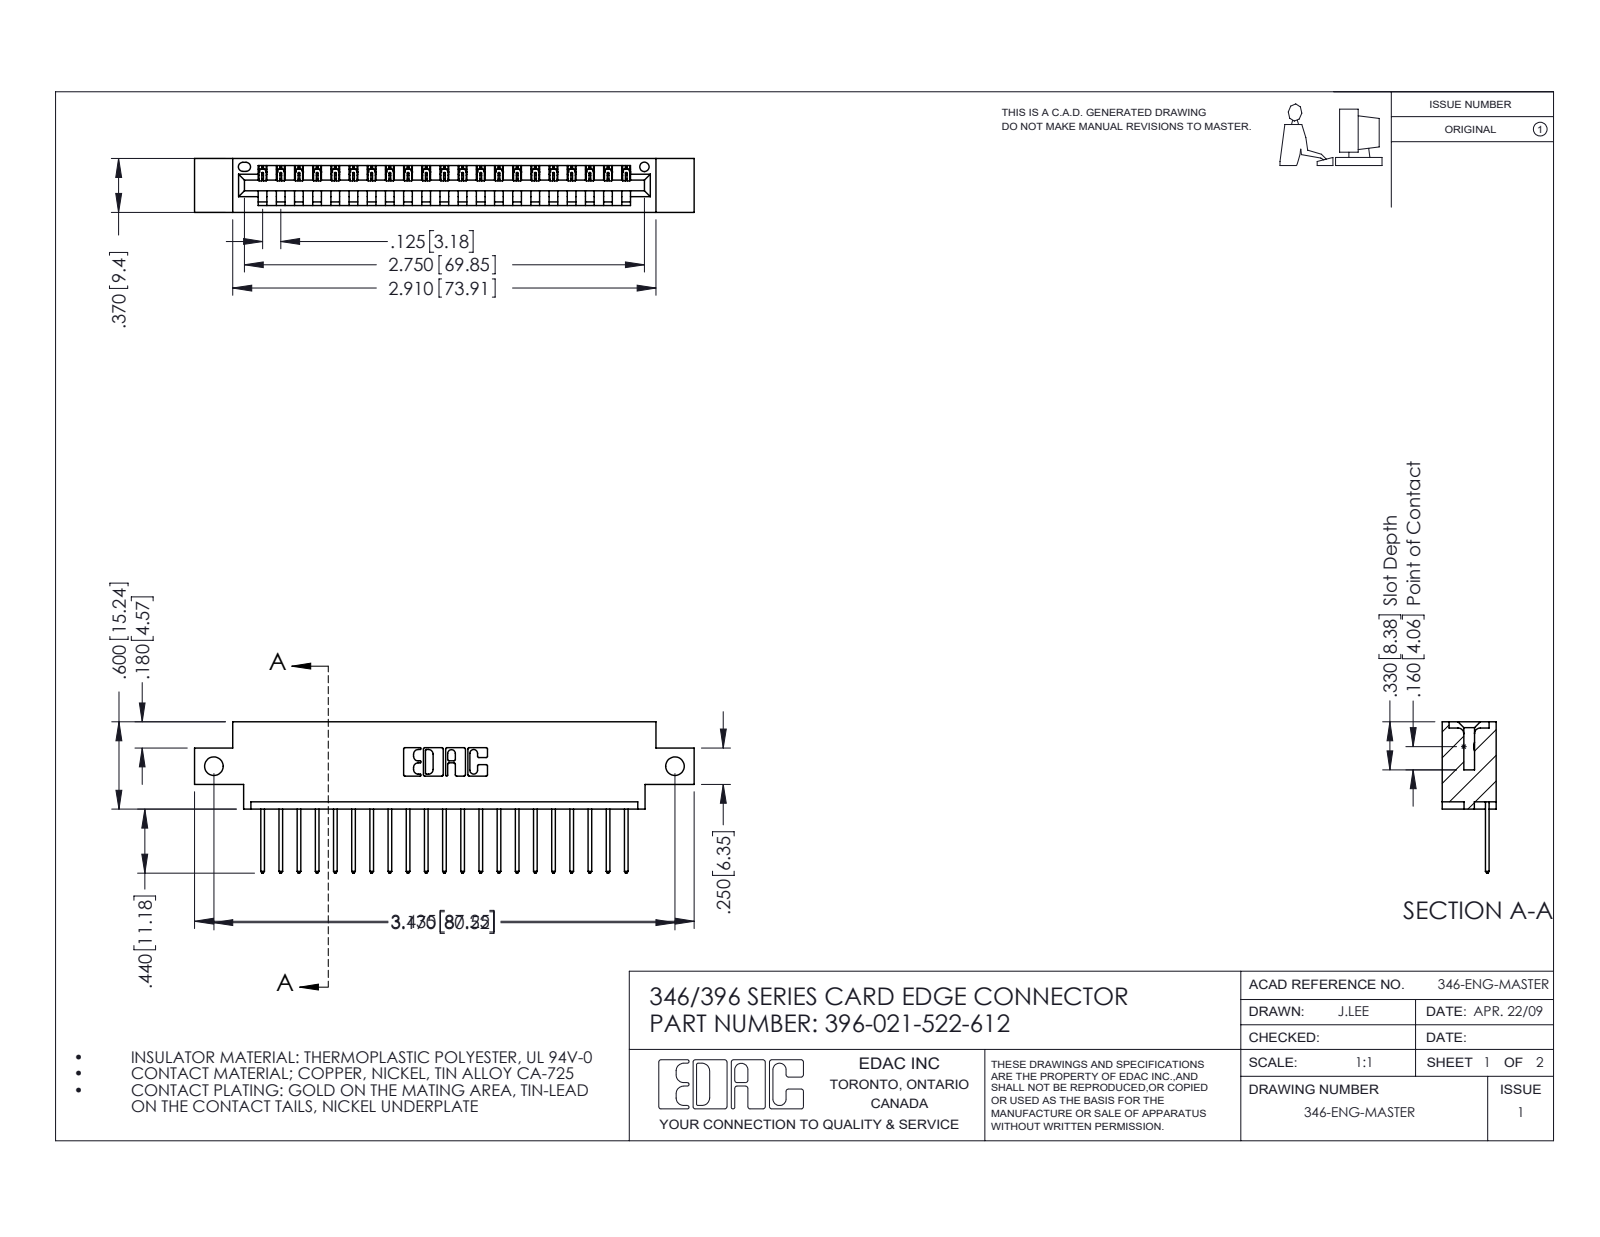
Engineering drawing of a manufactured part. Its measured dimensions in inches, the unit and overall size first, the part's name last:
Units: inches
Overall size (bounding box): 3.435 × 1.04 × 0.37
Round holes (diameter × count): ⌀0.128 ×2, ⌀0.064 ×1
Partial cylindrical surfaces — rounded edges, fillets, slot ends (radius × count): R0.006 ×42, R0.01 ×42, R0.01 ×22, R0.007 ×6, R0.031 ×6, R0.026 ×3, R0.031 ×2, R0.04 ×2
Main face-to-face distances: 0.048, 0.322, 0.37, 0.25, 0.072, 0.298, 0.025, 0.148, 0.222, 0.1
Hole centre spacings: 3.17
Volume: 0.486 in³ · Surface area: 15.23 in²
Bodies: 22 solids, 1344 faces (920 planar, 424 cylindrical, 0 other)
Part name (STEP PRODUCT): 345-292-001_345-293-122; 346 Part_0.170 Offset - Side Mount; 396-021-522-612
STEP written by: SolidWorks 2016 (CONFIG_CONTROL_DESIGN)
